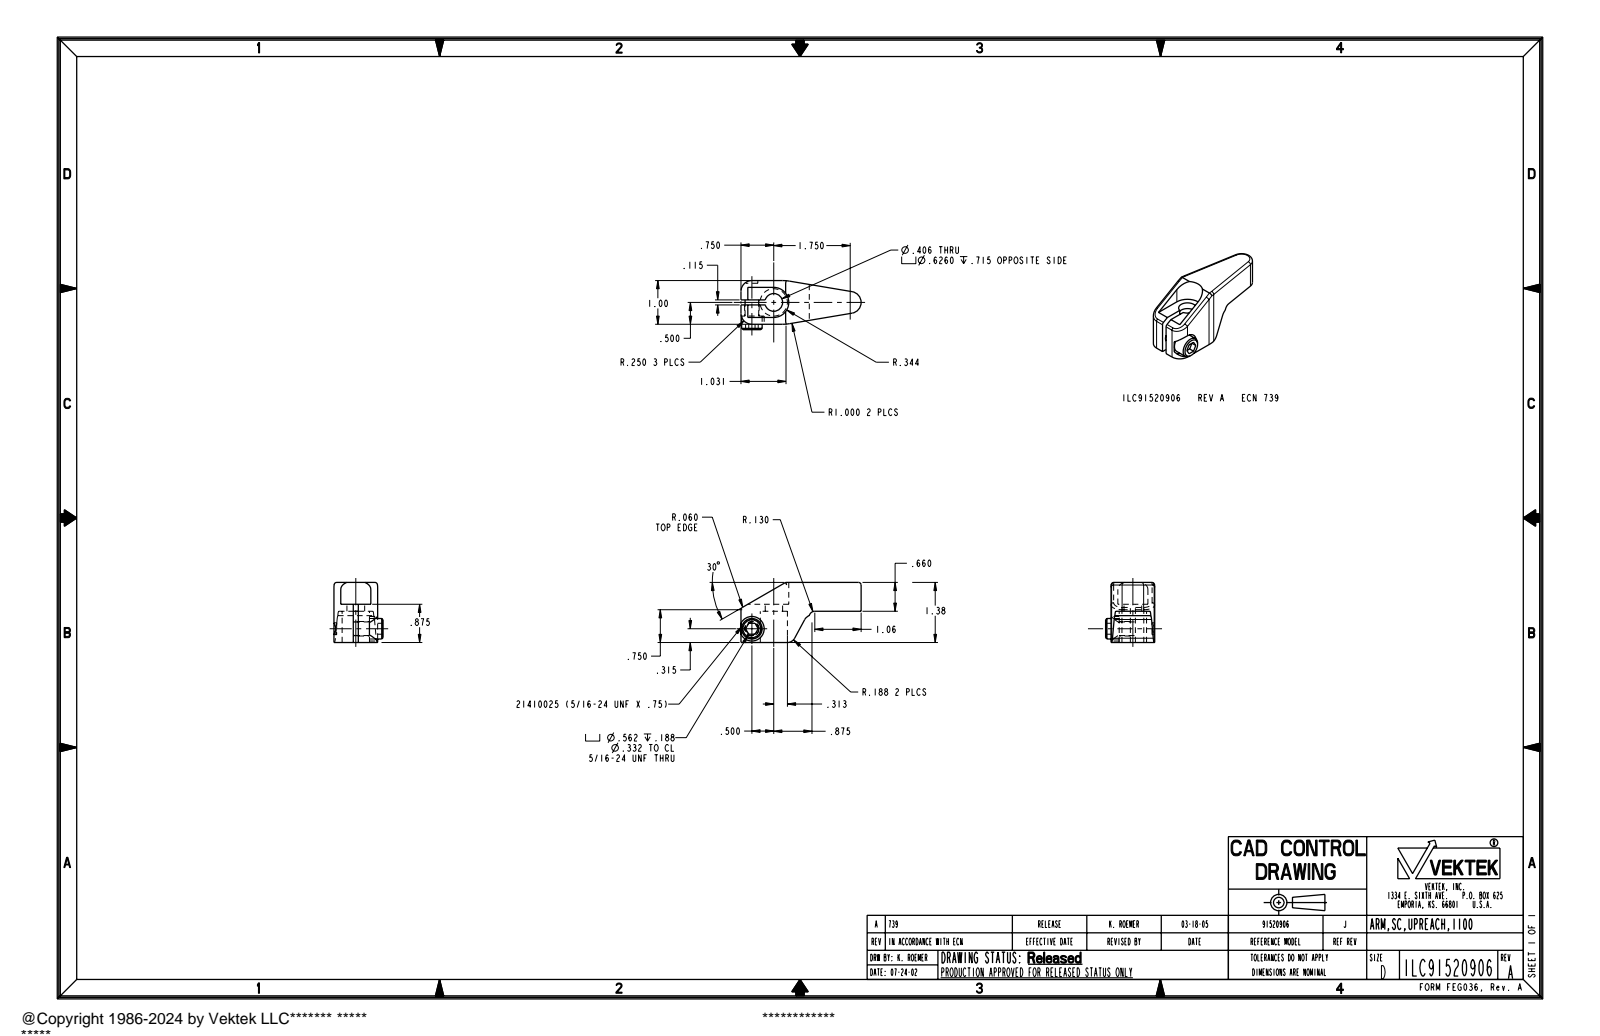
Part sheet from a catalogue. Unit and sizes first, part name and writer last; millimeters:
Units: millimetres
Overall size (bounding box): 69.9 × 34.9 × 28.5
Round holes (diameter × count): ⌀6.9 ×1, ⌀8.4 ×1, ⌀10.3 ×1, ⌀14.3 ×1, ⌀15.9 ×1
Round bosses / shafts (diameter × count): ⌀11.9 ×1, ⌀7.9 ×1
Partial cylindrical surfaces — rounded edges, fillets, slot ends (radius × count): R1.5 ×5, R6.4 ×3, R4.8 ×2, R25.4 ×2, R3.3 ×1, R8.7 ×1
Main face-to-face distances: 16.8, 34.9, 18.2, 11.3, 14.1, 25.4, 12.7, 4.1, 22.2, 2.9
Volume: 27 660 mm³ · Surface area: 9 219 mm²
Bodies: 1 solid, 65 faces (30 planar, 26 cylindrical, 9 other)
Part name (STEP PRODUCT): ILC91520906
STEP written by: PRO/ENGINEER BY PARAMETRIC TECHNOLOGY CORPORATION, 2004290 (AUTOMOTIVE_DESIGN_CC2)
